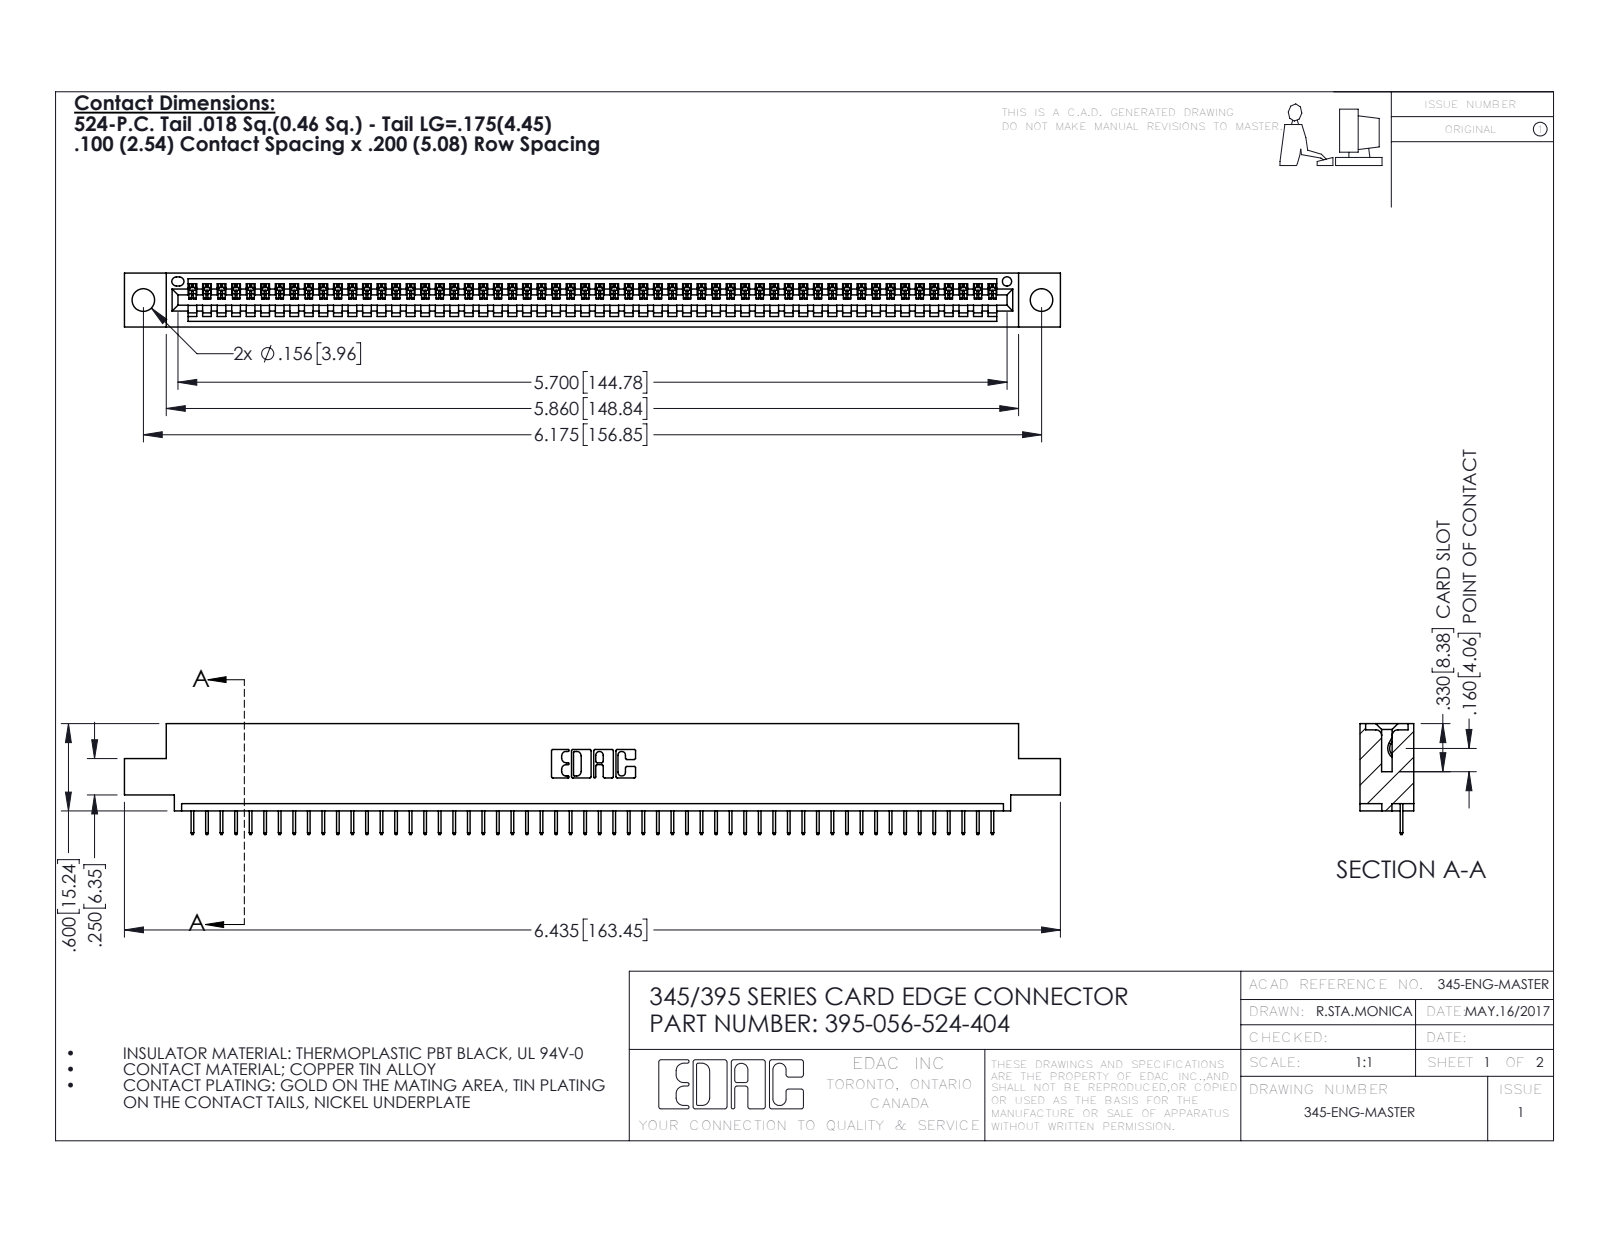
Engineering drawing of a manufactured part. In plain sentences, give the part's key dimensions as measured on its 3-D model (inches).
The part is named "395-056-524-404; 345-292-001_345-293-124; 345 Part_0.110 Offset - 0.156 Dia-TH". Its 3-D file was written by "SolidWorks 2016 (CONFIG_CONTROL_DESIGN)". It is 57 solids with 3602 faces: 2660 planar, 942 cylindrical and 0 other. Overall it measures 6.435 by 0.762 by 0.37 inches. Its volume is 0.931 cubic inches and its surface area 30.46 square inches. Round holes: 2 of diameter 0.156, 1 of diameter 0.064. Partial cylindrical surfaces (rounded edges, fillets, slot ends): 112 of radius 0.006, 22 of radius 0.01, 6 of radius 0.007, 6 of radius 0.031, 3 of radius 0.026, 2 of radius 0.031, 2 of radius 0.04, 1 of radius 0.014. The main face-to-face distances are 0.072, 0.298, 0.37, 0.2, 0.098, 0.272, 0.025, 0.225, 0.072, 0.149. The hole center spacings are 0.27, 5.939, 6.175.
